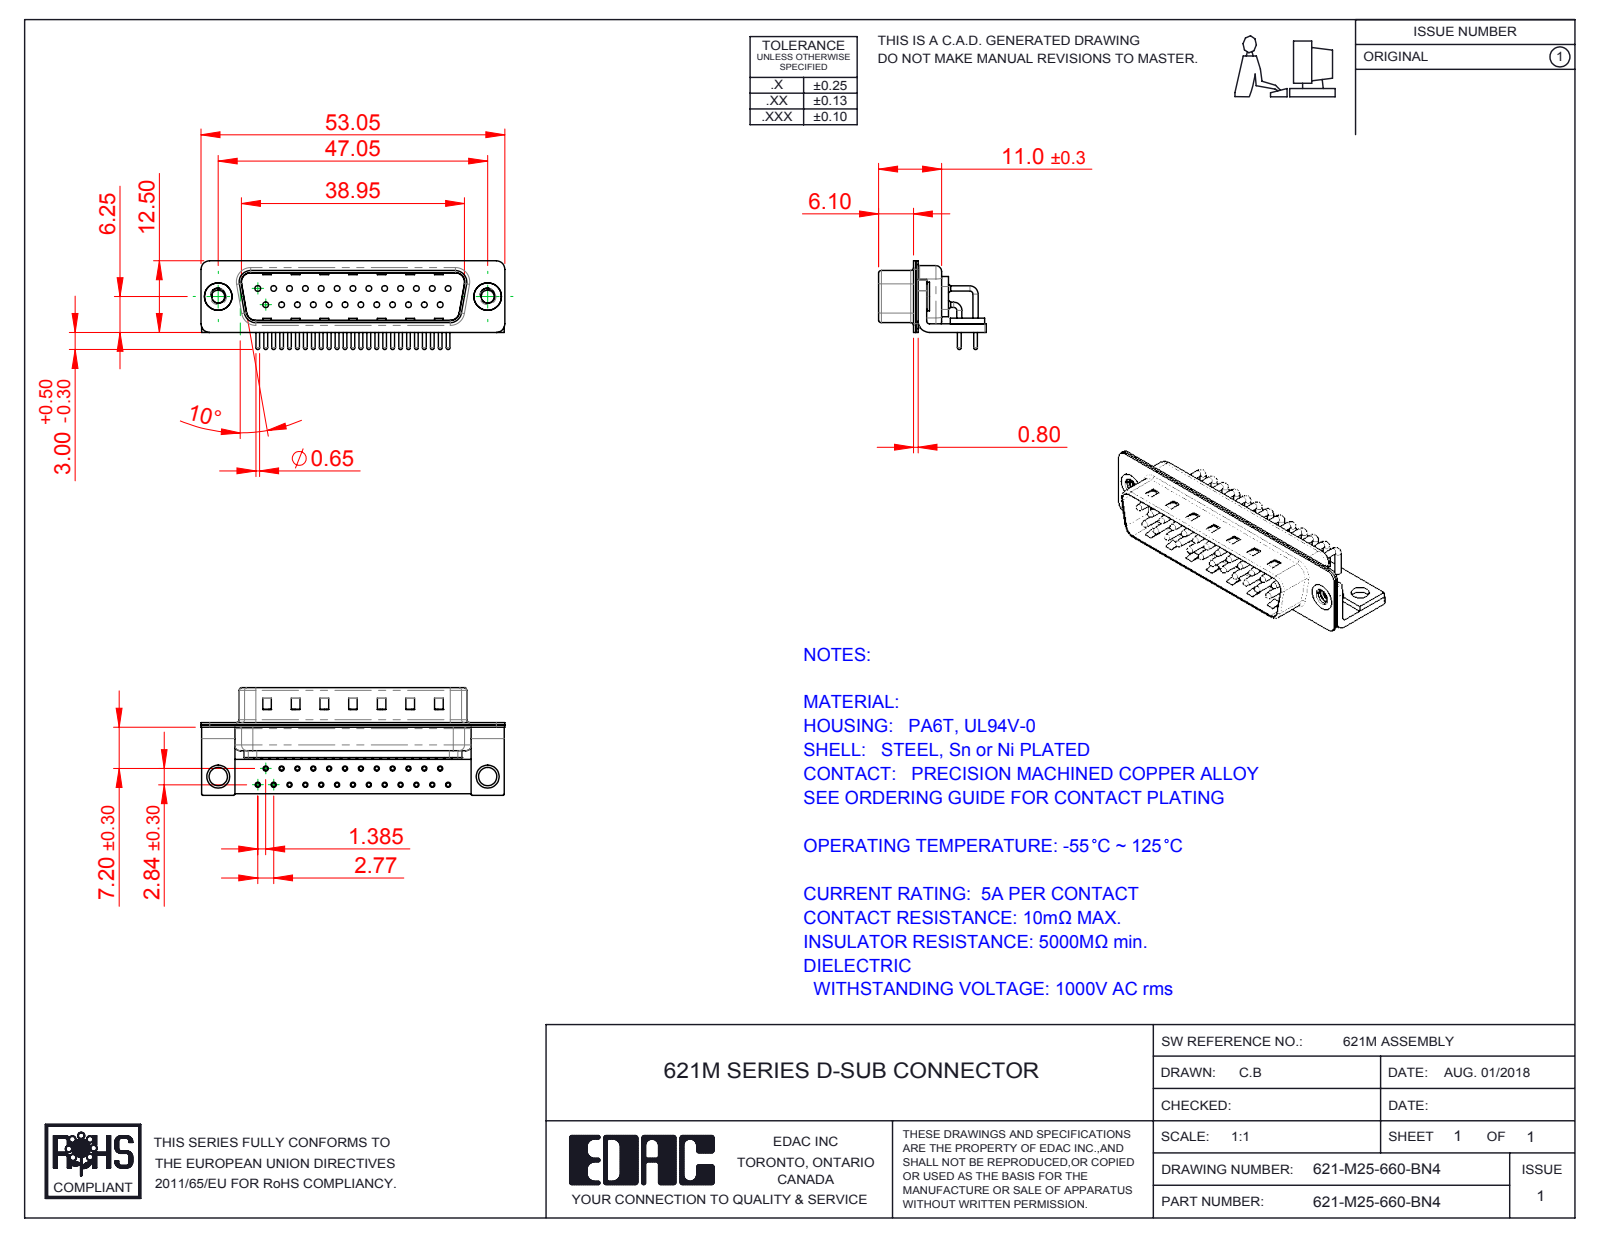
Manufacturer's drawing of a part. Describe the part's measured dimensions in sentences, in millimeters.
The part is named "621M Contact Row 2; 621M Contact Row 1; 621M Shell Rear_25 Contacts; 621M Housing_25 Contacts (+5 more)". Its 3-D file was written by "SolidWorks 2016 (CONFIG_CONTROL_DESIGN)". It is 33 solids with 3226 faces: 1797 planar, 1109 cylindrical and 320 other. Overall it measures 53.05 by 18.8 by 15.49 millimeters. Its volume is 3 385 cubic millimeters and its surface area 8 887 square millimeters. Round holes: 25 of diameter 0.9, 25 of diameter 1, 25 of diameter 1.7, 25 of diameter 2, 2 of diameter 2.26, 2 of diameter 3.2, 2 of diameter 4, 2 of diameter 4.8. Round bosses or shafts: 33 of diameter 0.9, 25 of diameter 1.5, 25 of diameter 0.65, 2 of diameter 5, 2 of diameter 4.9. Partial cylindrical surfaces (rounded edges, fillets, slot ends): 25 of radius 1.01, 16 of radius 0.25, 16 of radius 1.5, 13 of radius 2, 9 of radius 0.5, 8 of radius 1.6, 4 of radius 0.6, 4 of radius 0.65. The main face-to-face distances are 0.4, 0.85, 1.25, 1.5, 9.55, 0.8, 10.4, 1, 8.3, 8.7. The hole center spacings are 3.16, 2.77, 8.31, 5.54, 11.08, 13.85, 5.04, 16.62.
